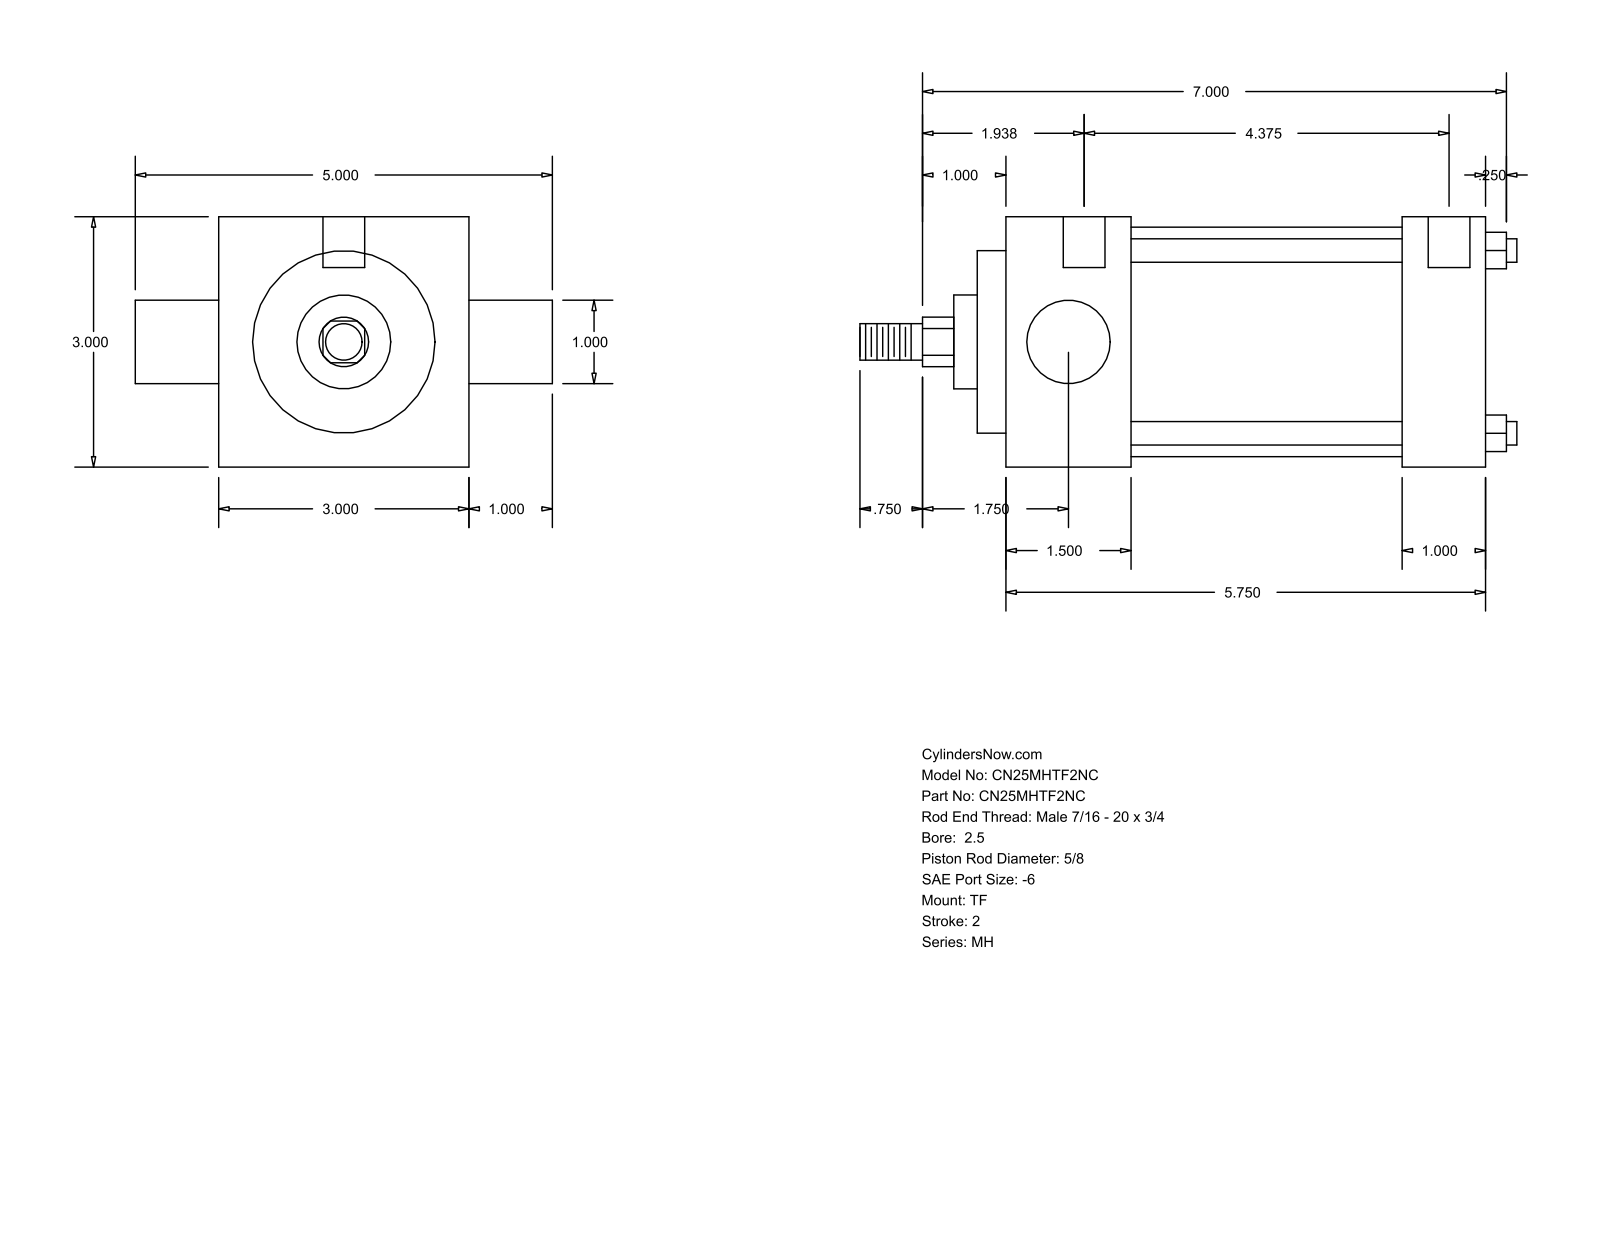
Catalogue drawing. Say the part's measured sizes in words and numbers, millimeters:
The part is named "MH_TF__0250_0.625". Its 3-D file was written by "GSSL Pune (CONFIG_CONTROL_DESIGN)". It is 0 solids with 86 faces: 61 planar, 25 cylindrical and 0 other. Overall it measures 200.03 by 127 by 76.2 millimeters. Round holes: 3 of diameter 5.56, 2 of diameter 12.7. Round bosses or shafts: 4 of diameter 7.14, 1 of diameter 69.85, 1 of diameter 55.55, 1 of diameter 28.57, 1 of diameter 25.4, 1 of diameter 15.88, 1 of diameter 11.11. Partial cylindrical surfaces (rounded edges, fillets, slot ends): 1 of radius 7.54. The main face-to-face distances are 76.2, 146.05, 25.4, 82.55, 38.1, 107.95, 120.65, 8.73, 46.83, 129.38. The hole center spacings are 3.17, 4.76, 111.13, 114.3, 115.89, 119.06.
